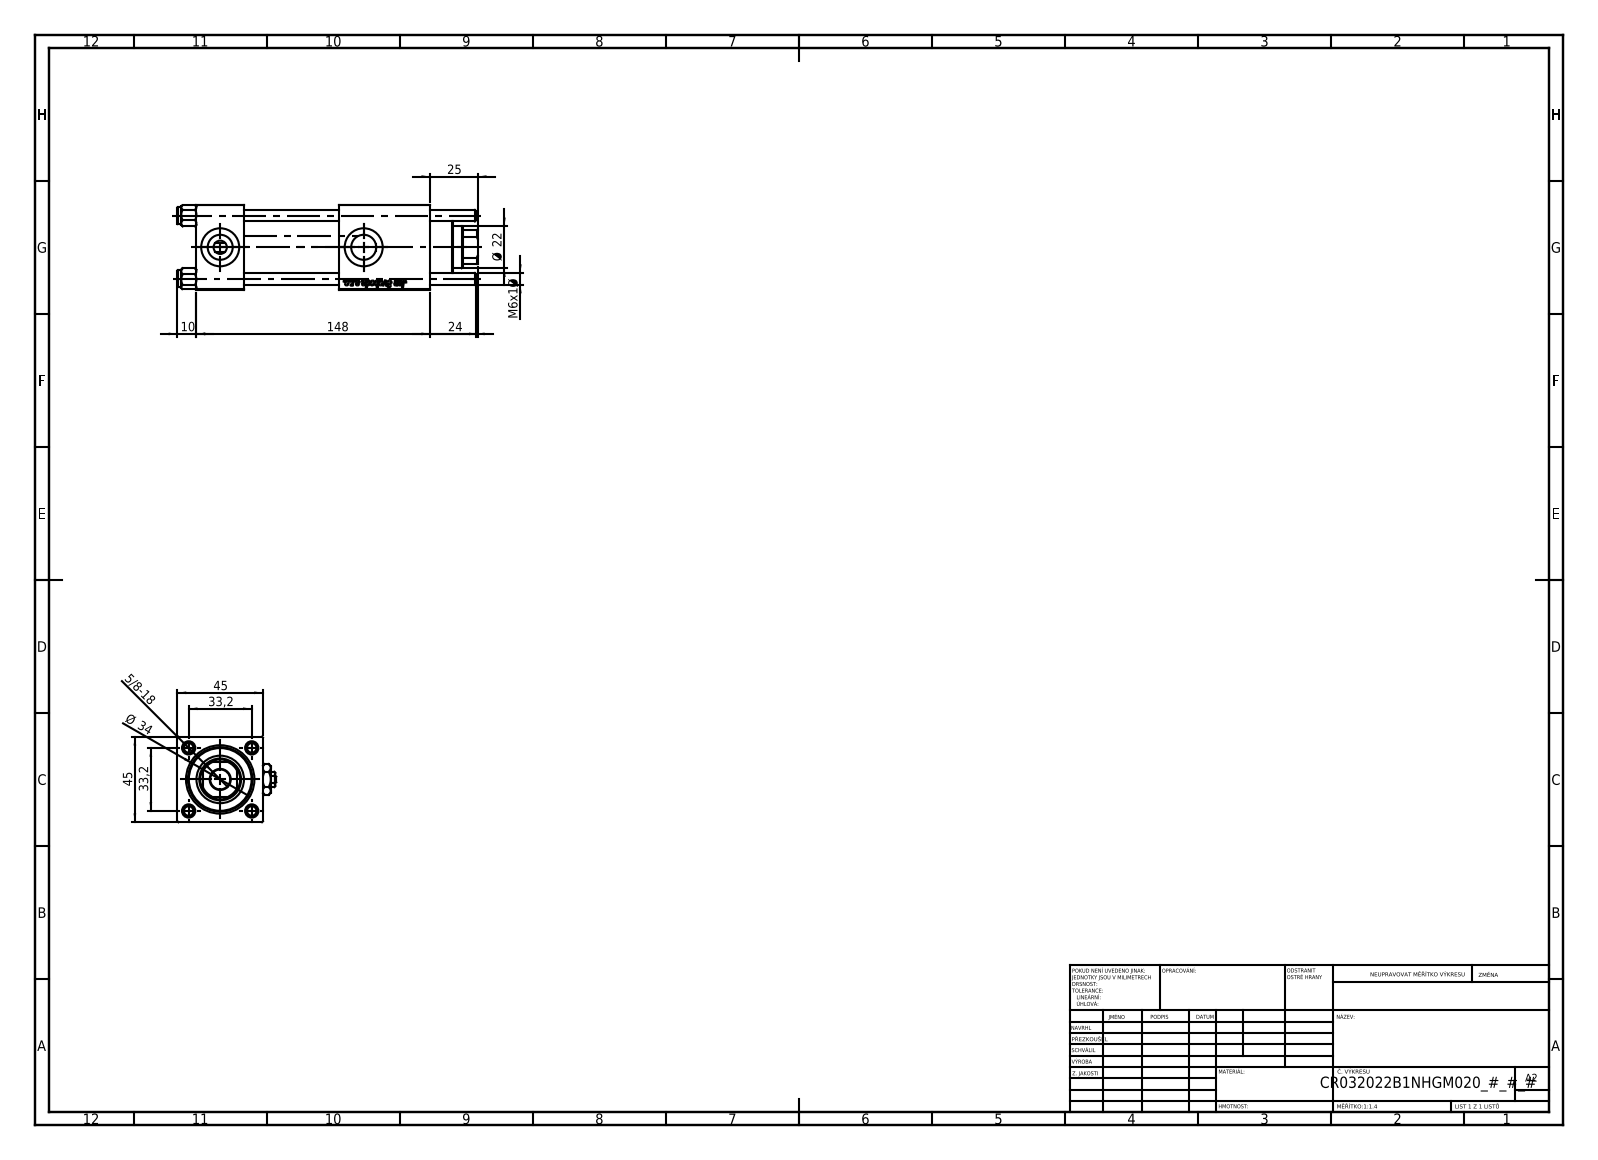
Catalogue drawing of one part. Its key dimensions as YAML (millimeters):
part_name: "V215CR_B-1; V215CR_B_TYCINKA; Zatka_pro_OIL_PORT; V215_VC_A (+2 more)"
step_written_by: "SolidWorks 2019 (CONFIG_CONTROL_DESIGN)"
units: millimeters
bodies: {solids: 12, faces: 1205, planar: 455, cylindrical: 82, other: 668}
overall_size: [158, 52, 45]
volume: 213630
surface_area: 77550
round_holes:
  - {diameter: 6, count: 4}
  - {diameter: 7, count: 2}
  - {diameter: 13.16, count: 2}
  - {diameter: 20, count: 2}
  - {diameter: 10.5, count: 1}
  - {diameter: 22, count: 1}
  - {diameter: 24, count: 1}
  - {diameter: 25, count: 1}
  - {diameter: 32, count: 1}
  - {diameter: 33, count: 1}
round_bosses_or_shafts:
  - {diameter: 9, count: 4}
  - {diameter: 38, count: 1}
  - {diameter: 34, count: 1}
partial_cylinders:
  - {radius: 10.5, count: 1}
face_to_face_distances: [45, 25, 50, 123, 75, 98, 48, 94.3, 69.3, 19.3]
hole_center_spacings: [23.48, 33.2, 46.95, 75.5]
